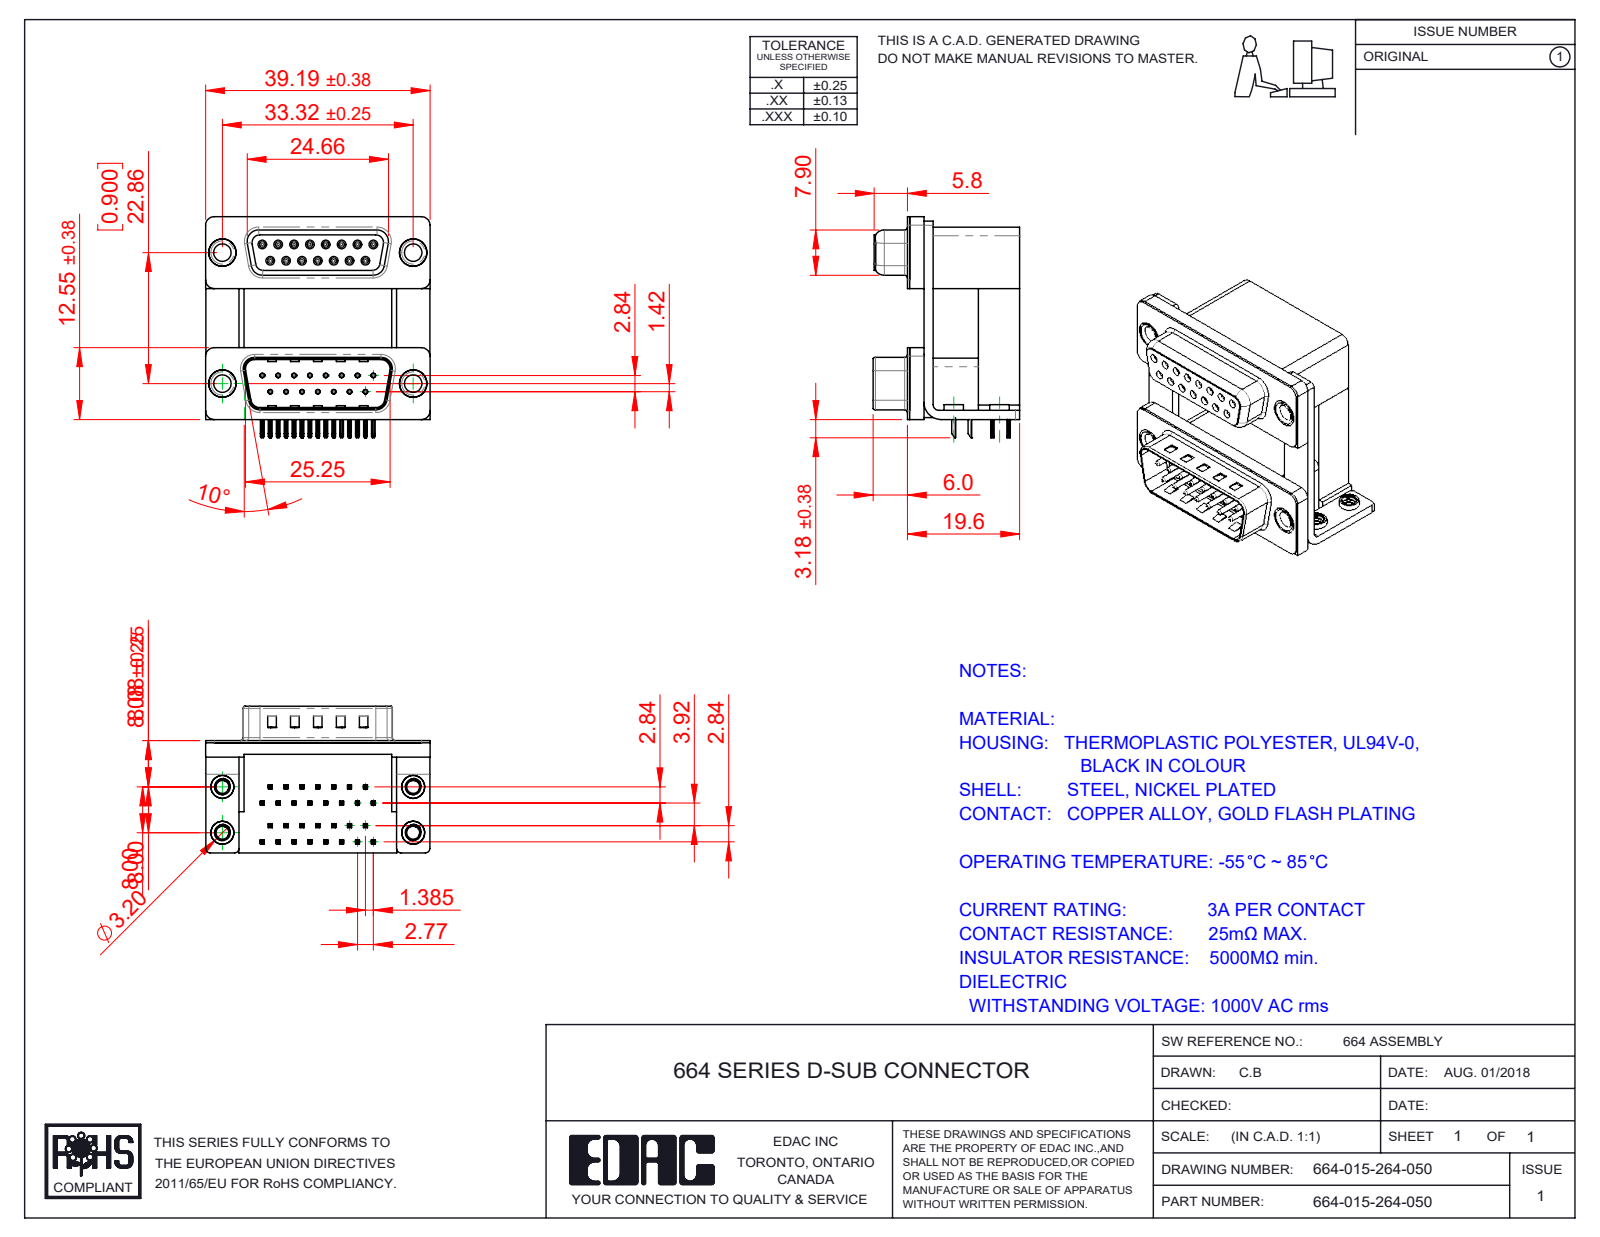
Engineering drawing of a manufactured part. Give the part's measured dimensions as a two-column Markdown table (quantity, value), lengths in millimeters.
| quantity | value |
| --- | --- |
| part name | 664 Mounting Bracket_ThruH; 664 Contact Bottom Upper_H; 664 Contact Top Lower; 664 4-40 Threaded Board Mount (+8 more) |
| STEP written by | SolidWorks 2020 (CONFIG_CONTROL_DESIGN) |
| units | millimeters |
| bodies | 45 solids, 3968 faces (2027 planar, 1054 cylindrical, 887 other) |
| overall size | 39.19 × 38.59 × 25.6 |
| volume | 15 948 mm³ |
| surface area | 17 759 mm² |
| round holes (diameter × count) | 0.8 × 30, 0.35 × 15, 0.9 × 15, 2.26 × 4, 2.75 × 4, 3.05 × 4, 3.2 × 4, 3.5 × 4, 4 × 4, 4.8 × 4, 5 × 4 |
| round bosses / shafts (diameter × count) | 1.2 × 15, 0.75 × 15, 4.9 × 4, 4.75 × 4, 4 × 4, 3.85 × 4, 3.4 × 4 |
| partial cylindrical surfaces (radius × count) | 0.1 × 120, 0.15 × 60, 0.25 × 60, 0.12 × 30, 0.35 × 30, 1.5 × 16, 0.34 × 15, 0.5 × 12 |
| main face-to-face distances | 0.4, 19.2, 12, 7.2, 16.7, 9.5, 2.5, 2.19, 12.4, 22.86 |
| hole center spacings | 3.16, 2.77, 23.03, 5.54, 23.52, 8.31, 22.86, 24.32 |
